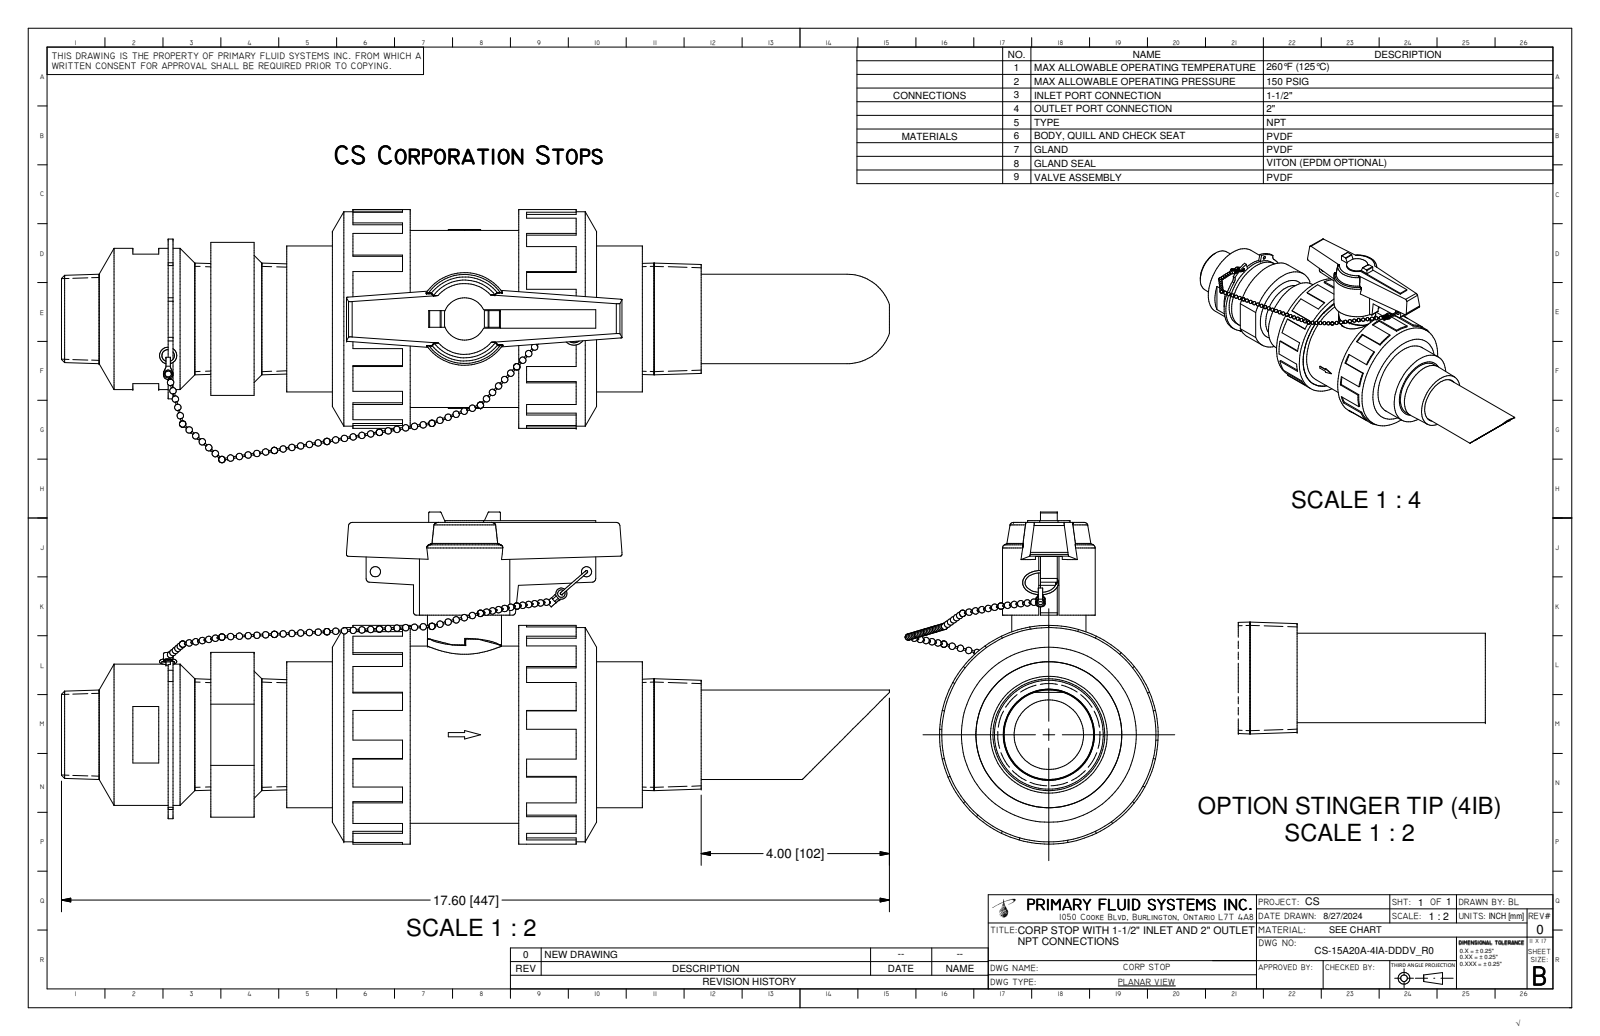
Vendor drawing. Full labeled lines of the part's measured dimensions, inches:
STEP written by: Autodesk Inventor 2025 (CONFIG_CONTROL_DESIGN)
Units: inches
Bodies: 19 solids, 539 faces (308 planar, 131 cylindrical, 100 other)
Overall size (bounding box): 17.595 × 7.054 × 5.377
Volume: 109.5 in³ · Surface area: 598.2 in²
Round holes (diameter × count): ⌀0.118 ×2, ⌀0.15 ×2, ⌀0.157 ×2, ⌀0.217 ×2, ⌀1.476 ×1, ⌀1.5 ×1, ⌀1.93 ×1, ⌀1.939 ×1, ⌀1.969 ×1, ⌀2.375 ×1, ⌀2.48 ×1, ⌀2.982 ×1
Round bosses / shafts (diameter × count): ⌀0.035 ×9, ⌀0.236 ×2, ⌀4.646 ×1, ⌀4.553 ×1, ⌀4.18 ×1, ⌀3.762 ×1, ⌀3.1 ×1, ⌀3 ×1
Partial cylindrical surfaces — rounded edges, fillets, slot ends (radius × count): R0.02 ×4, R0.059 ×4, R0.079 ×4, R0.039 ×2, R0.098 ×2, R0.236 ×2, R0.45 ×1, R1.698 ×1
Main face-to-face distances: 4.933, 1.313, 1.313, 3.62, 3.619, 2.626, 0.34, 0.341, 1.654, 3.96
Hole centre spacings: 1.638, 0.314, 0.708, 1.24, 1.545, 1.844, 3.98, 4.487
